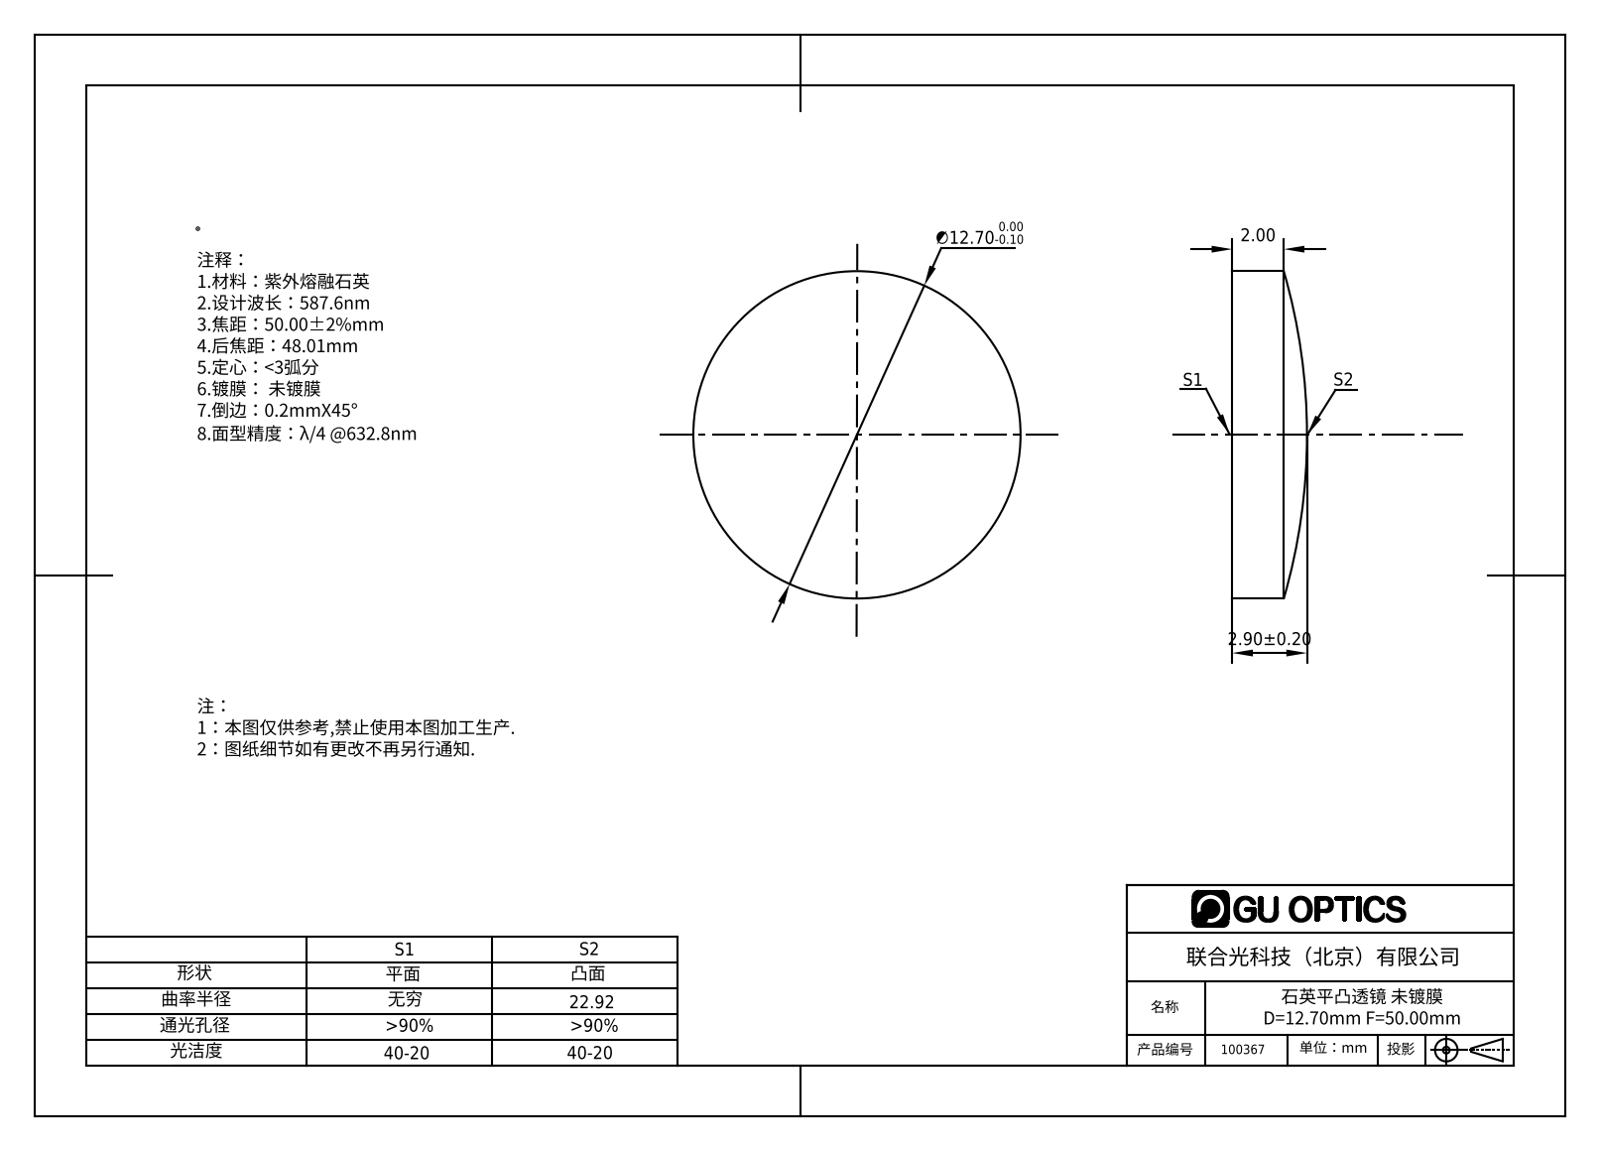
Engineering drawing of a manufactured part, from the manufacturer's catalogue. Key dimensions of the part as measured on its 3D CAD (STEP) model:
Part name (STEP PRODUCT): 100367
STEP written by: SolidWorks 2016 (AUTOMOTIVE_DESIGN)
Units: millimetres
Bodies: 1 solid, 5 faces (1 planar, 2 cylindrical, 2 other)
Overall size (bounding box): 12.7 × 12.7 × 2.9
Volume: 311 mm³ · Surface area: 336 mm²
Round bosses / shafts (diameter × count): ⌀12.7 ×1
